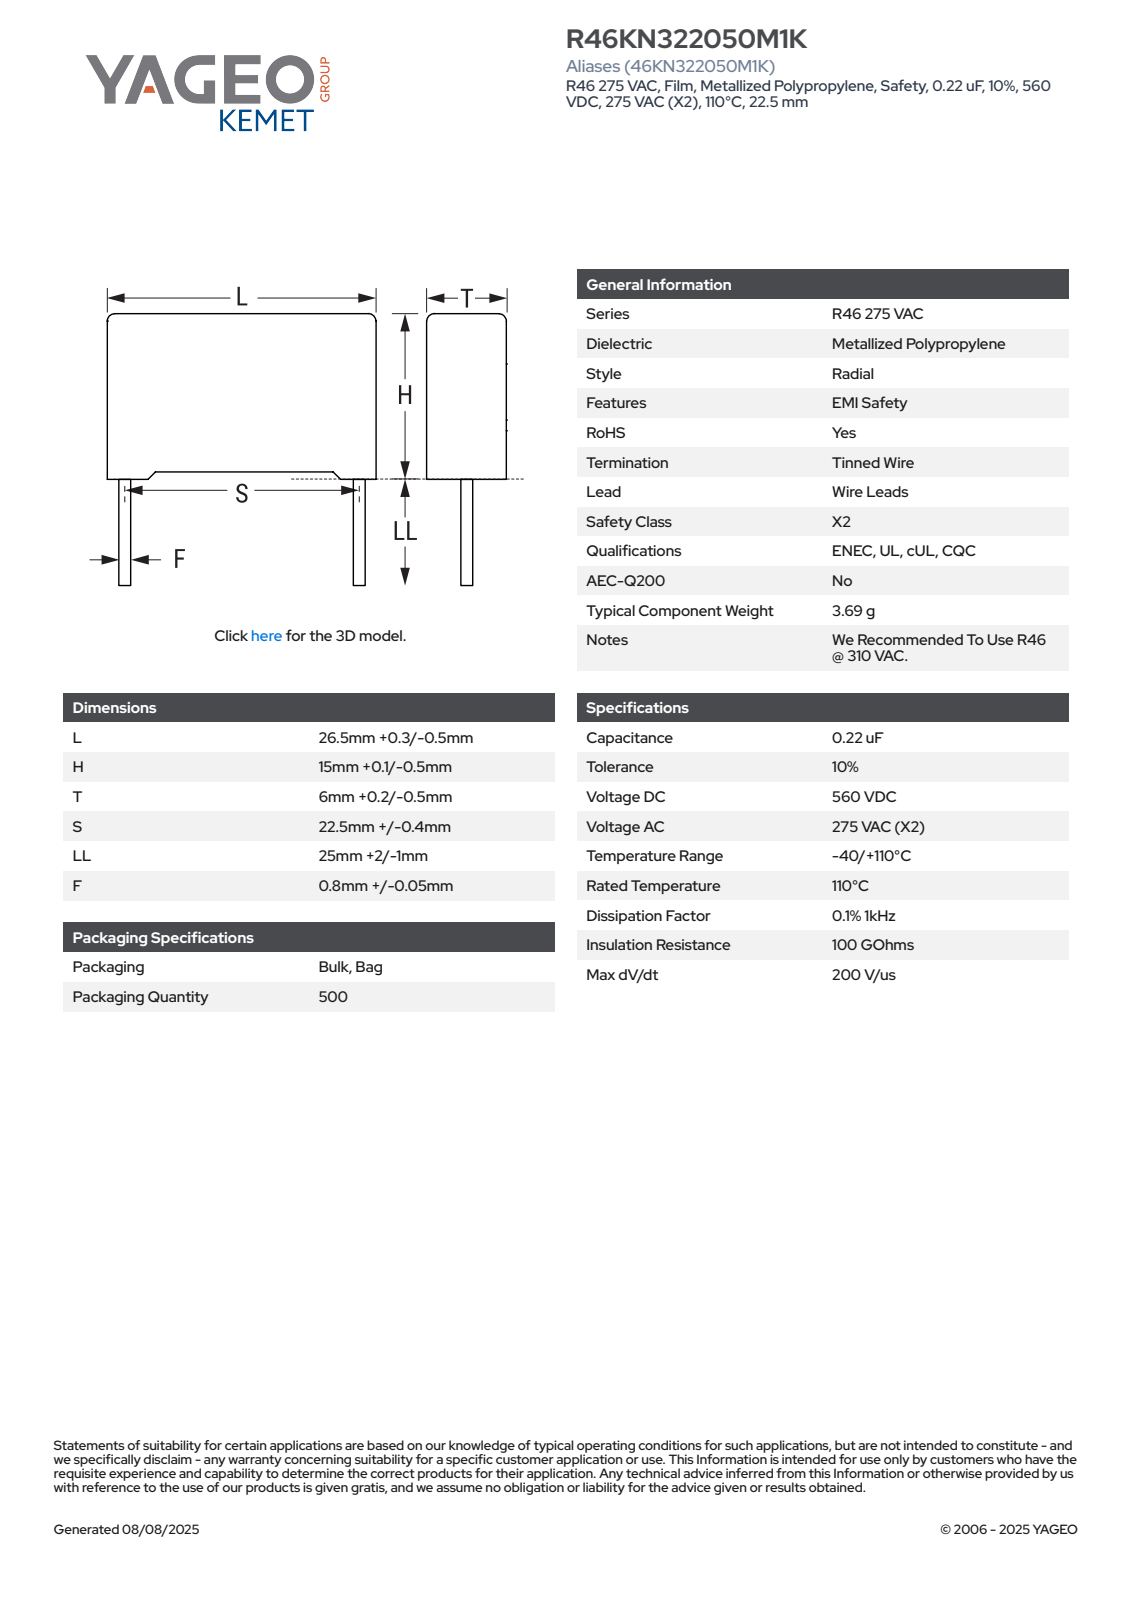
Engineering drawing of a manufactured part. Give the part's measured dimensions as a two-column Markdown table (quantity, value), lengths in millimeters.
| quantity | value |
| --- | --- |
| part name | CFR_RB2_26.5X15X6_L26.8H15.1T6.2S22.5LL27F0.85 |
| STEP written by | SolidWorks 2021 (AUTOMOTIVE_DESIGN) |
| units | millimeters |
| bodies | 4 solids, 85 faces (77 planar, 8 cylindrical, 0 other) |
| overall size | 42.1 × 26.8 × 6.21 |
| volume | 2 437 mm³ |
| surface area | 1 522 mm² |
| round bosses / shafts (diameter × count) | 0.85 × 2 |
| partial cylindrical surfaces (radius × count) | 0.5 × 4 |
| main face-to-face distances | 6.2, 14.35, 26.8, 14.58, 0.89, 0.52, 0.75, 15.1, 5.31, 4.42 |
